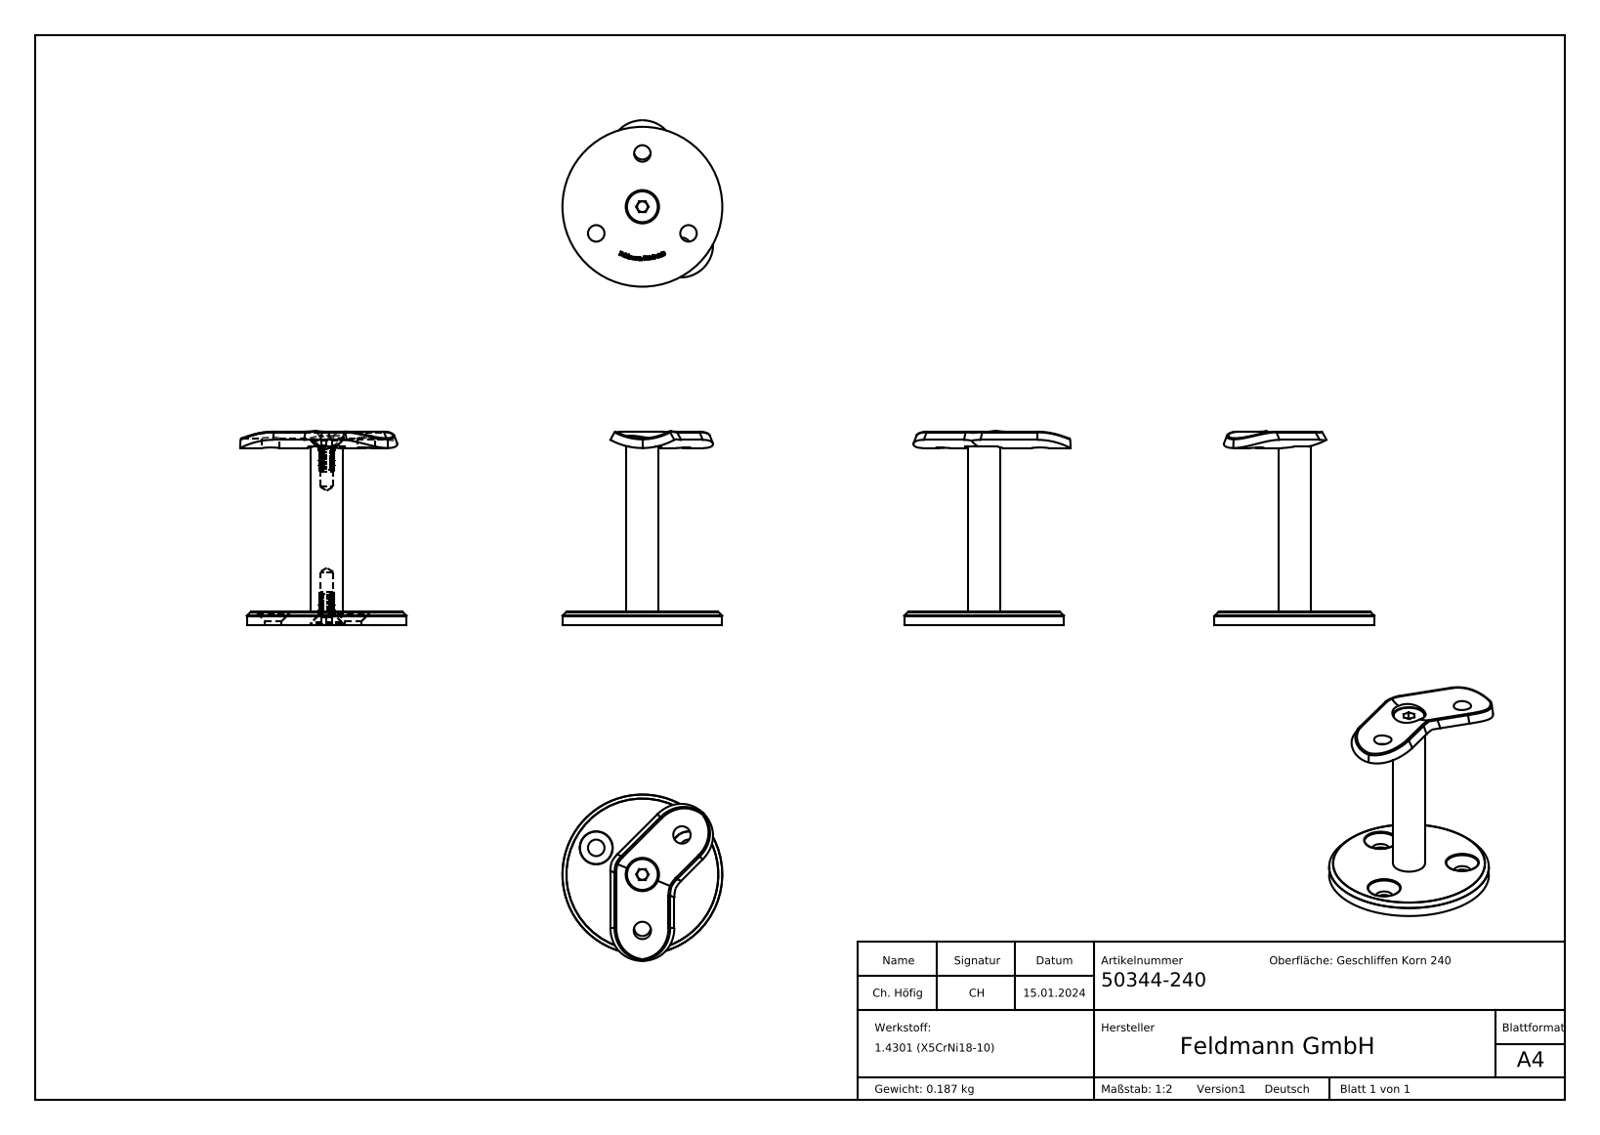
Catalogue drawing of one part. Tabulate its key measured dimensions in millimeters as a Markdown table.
| quantity | value |
| --- | --- |
| part name | 50344-240; 5034X-240 Teil2_5034X-240 Teil2; 50344-240 Teil3_50344-240 Teil3; socket countersunk head screw_din_DIN 7991 - M6 x 12 --- 12S (+1 more) |
| STEP written by | SolidWorks 2018 (CONFIG_CONTROL_DESIGN) |
| units | millimeters |
| bodies | 5 solids, 385 faces (163 planar, 50 cylindrical, 172 other) |
| overall size | 72.95 × 62.49 × 60 |
| volume | 24 324 mm³ |
| surface area | 13 880 mm² |
| round holes (diameter × count) | 6.2 × 3, 6.5 × 3, 12.2 × 3, 5 × 1, 8.2 × 1, 12.5 × 1 |
| round bosses / shafts (diameter × count) | 60 × 1, 12 × 1, 11.57 × 1, 6 × 1 |
| partial cylindrical surfaces (radius × count) | 0.5 × 4, 12.5 × 4, 10 × 2, 21.2 × 2, 24.9 × 2, 7.1 × 1 |
| main face-to-face distances | 5, 67, 62, 0.45, 69.7, 4.55, 66.55, 69.25, 64.7, 2.7 |
| hole center spacings | 20, 34.64, 21, 35.51, 1, 5.44, 32.53, 37.88 |
